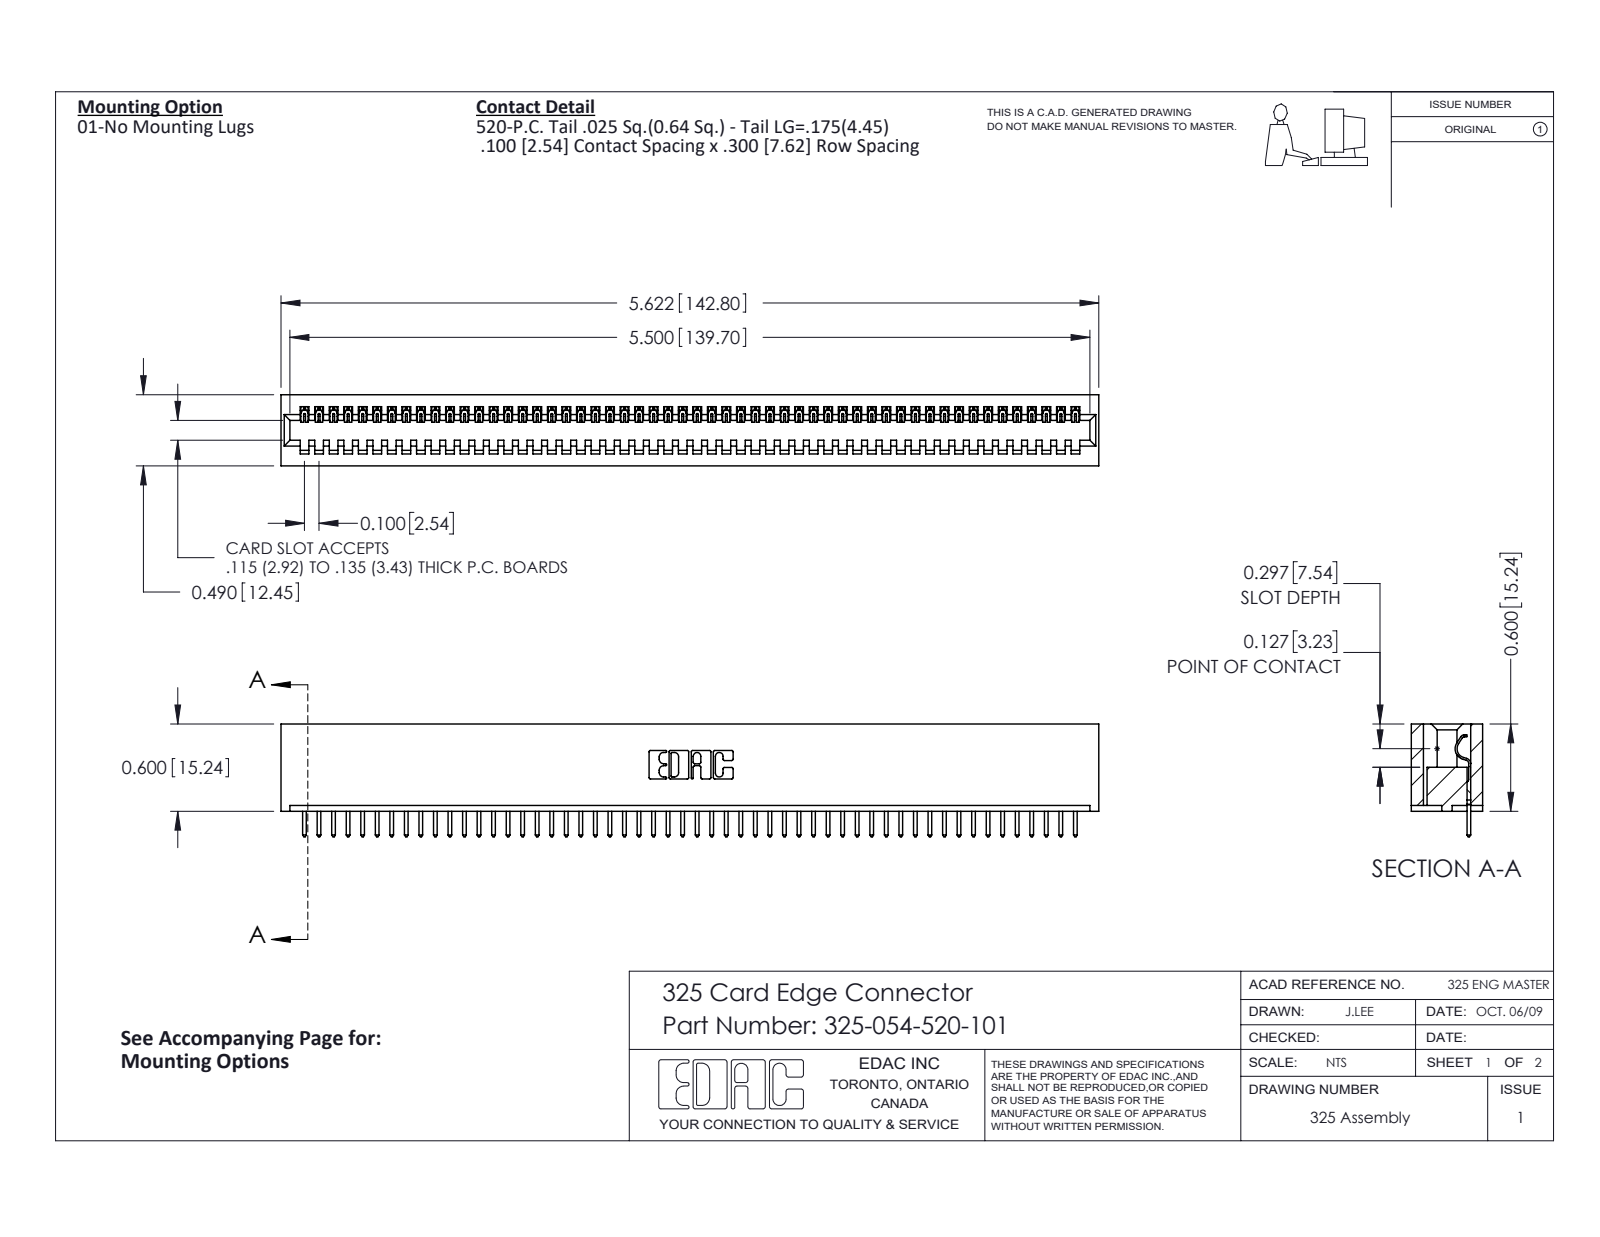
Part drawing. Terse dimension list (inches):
name: 325 Part_Lugless; 325-292-001_325-293-120; 325-054-520-101
written by: SolidWorks 2016 (CONFIG_CONTROL_DESIGN)
unit: in
bodies: 55 solids, 3238 faces (2334 planar, 904 cylindrical, 0 other)
size: 5.622 × 0.775 × 0.49
volume: 1.138 in³; area: 31.79 in²
rounds: 108× R0.006, 108× R0.01, 22× R0.01, 6× R0.007, 6× R0.031, 3× R0.026, 1× R0.014, 1× R0.022
face distances: 0.083, 0.407, 0.49, 0.3, 0.107, 0.383, 0.025, 0.325, 0.56, 0.263
